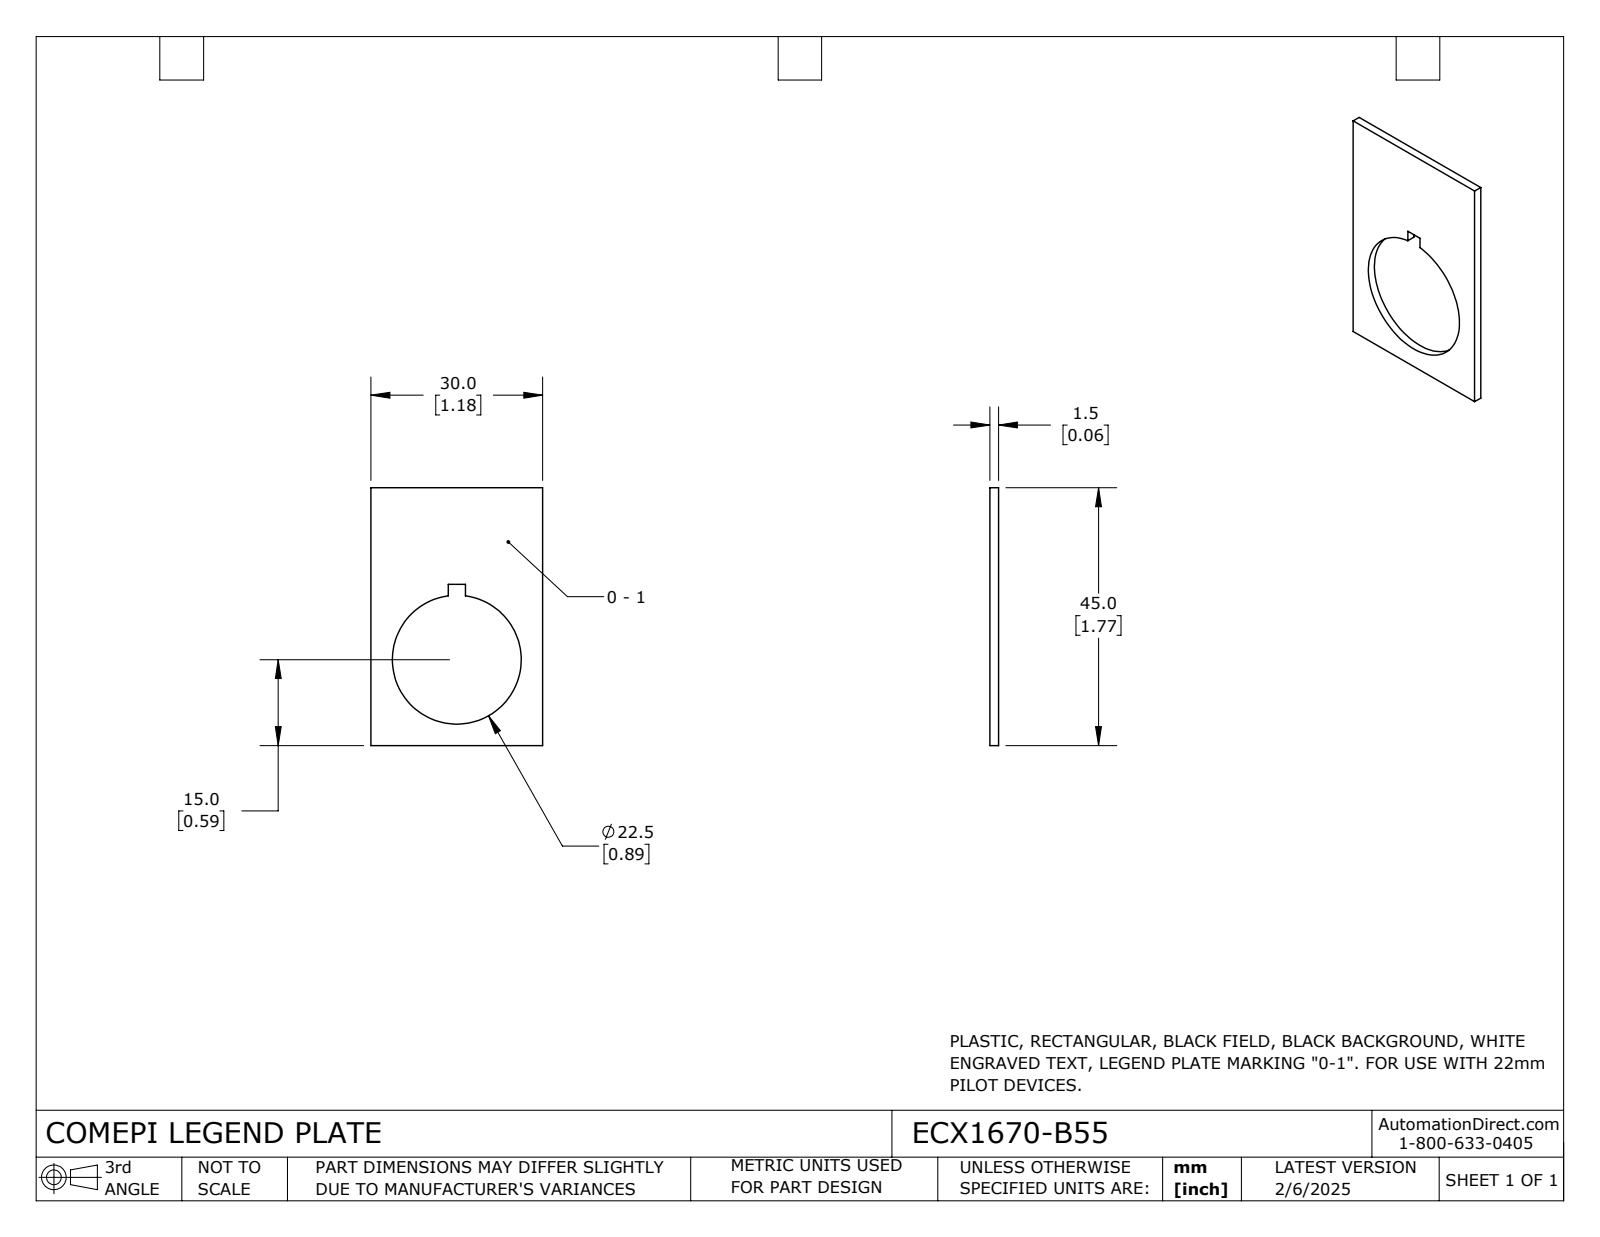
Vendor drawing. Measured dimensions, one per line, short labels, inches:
name: ECX1670-B55
written by: SolidWorks 2024 (CONFIG_CONTROL_DESIGN)
unit: in
bodies: 1 solid, 12 faces (9 planar, 3 cylindrical, 0 other)
size: 1.772 × 1.181 × 0.059
volume: 0.087 in³; area: 3.457 in²
holes: 1× ⌀0.886
face distances: 0.059, 1.181, 1.772, 0.531, 0.65, 1.108, 0.663, 0.118
